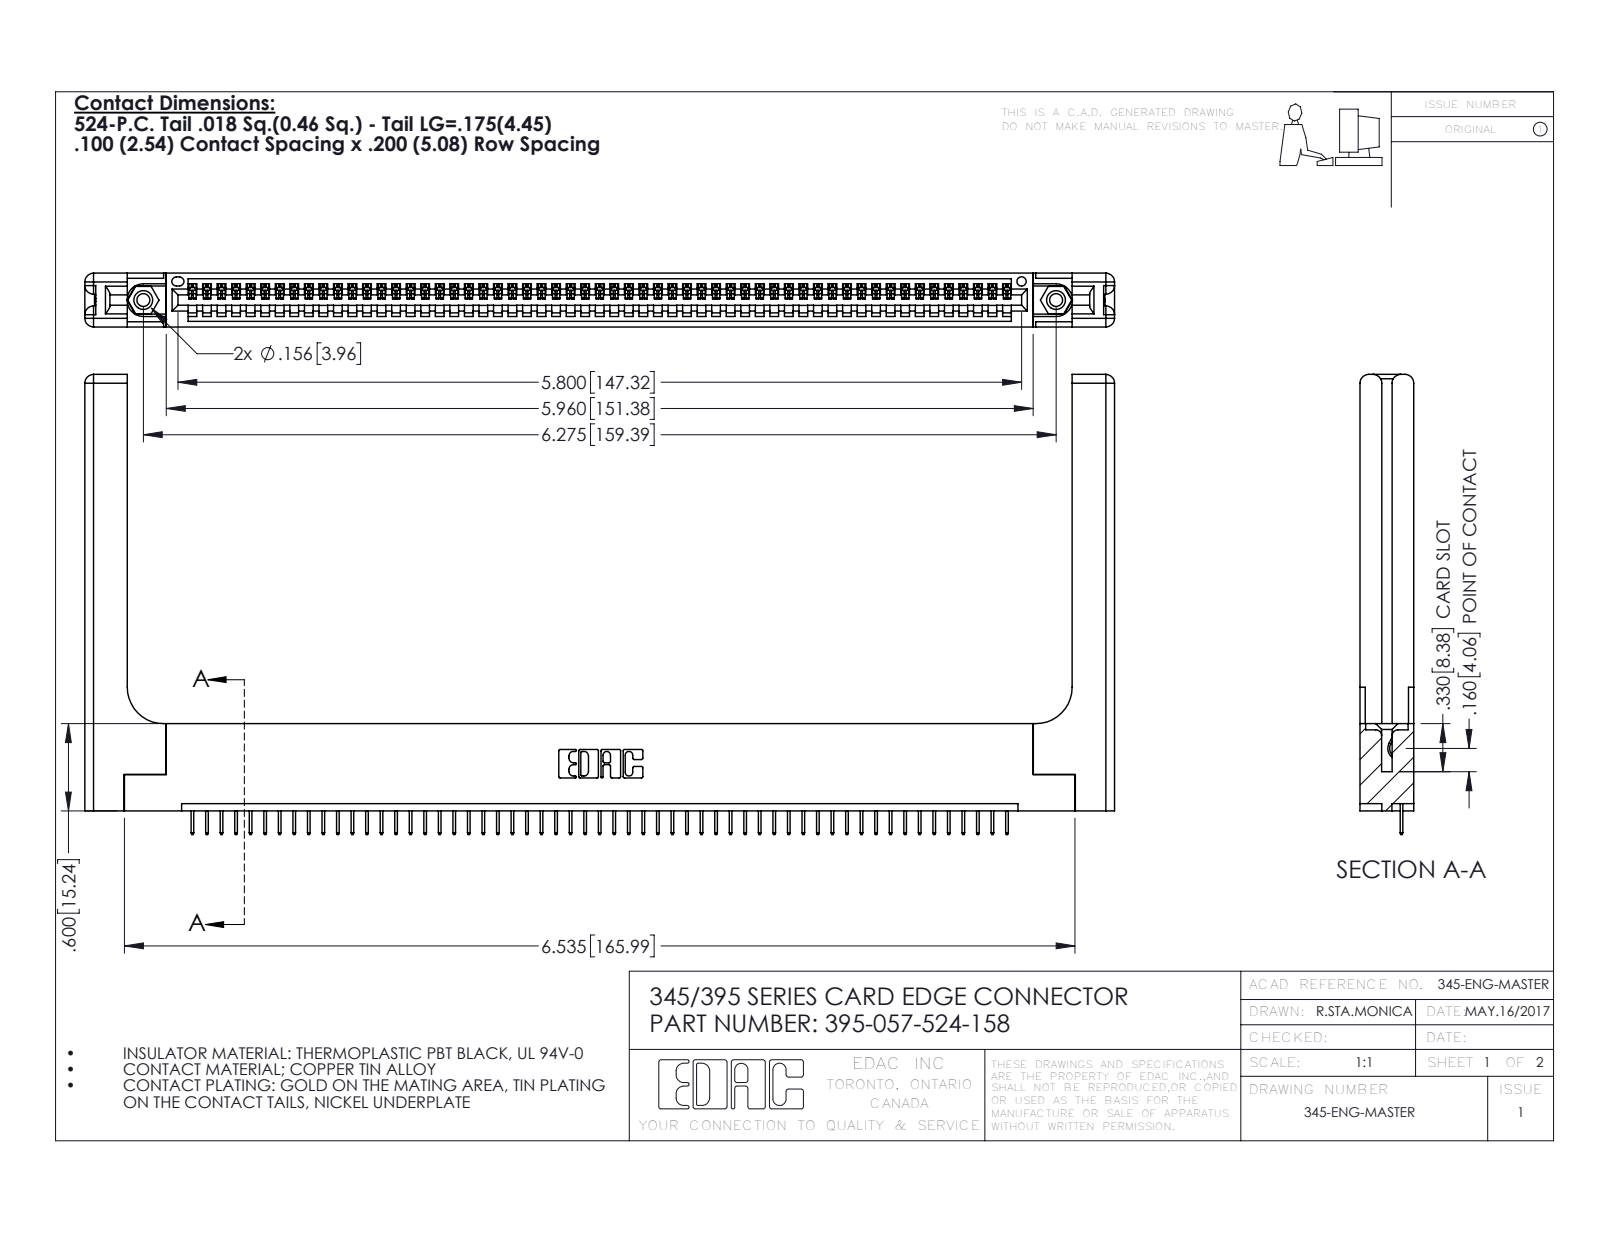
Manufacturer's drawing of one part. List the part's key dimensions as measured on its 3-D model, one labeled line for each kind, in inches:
Part name (STEP PRODUCT): 345-292-001_345-293-124; 345 Part_Flush Mounting Lugs - 0.156 Dia-TH; 395-057-524-158; 345-220-058_345-220-058 (+1 more)
STEP written by: SolidWorks 2016 (CONFIG_CONTROL_DESIGN)
Units: inches
Bodies: 62 solids, 3916 faces (2850 planar, 1006 cylindrical, 60 other)
Overall size (bounding box): 7.079 × 3.162 × 0.37
Volume: 1.555 in³ · Surface area: 42.39 in²
Round holes (diameter × count): ⌀0.089 ×2, ⌀0.125 ×2, ⌀0.156 ×2, ⌀0.064 ×1
Round bosses / shafts (diameter × count): ⌀0.155 ×2
Partial cylindrical surfaces — rounded edges, fillets, slot ends (radius × count): R0.006 ×114, R0.01 ×22, R0.06 ×16, R0.007 ×6, R0.031 ×6, R0.026 ×3, R0.03 ×2, R0.031 ×2
Main face-to-face distances: 0.37, 0.072, 0.298, 0.2, 0.098, 0.272, 0.025, 0.225, 0.148, 0.15
Hole centre spacings: 0.27, 6.039, 6.275
